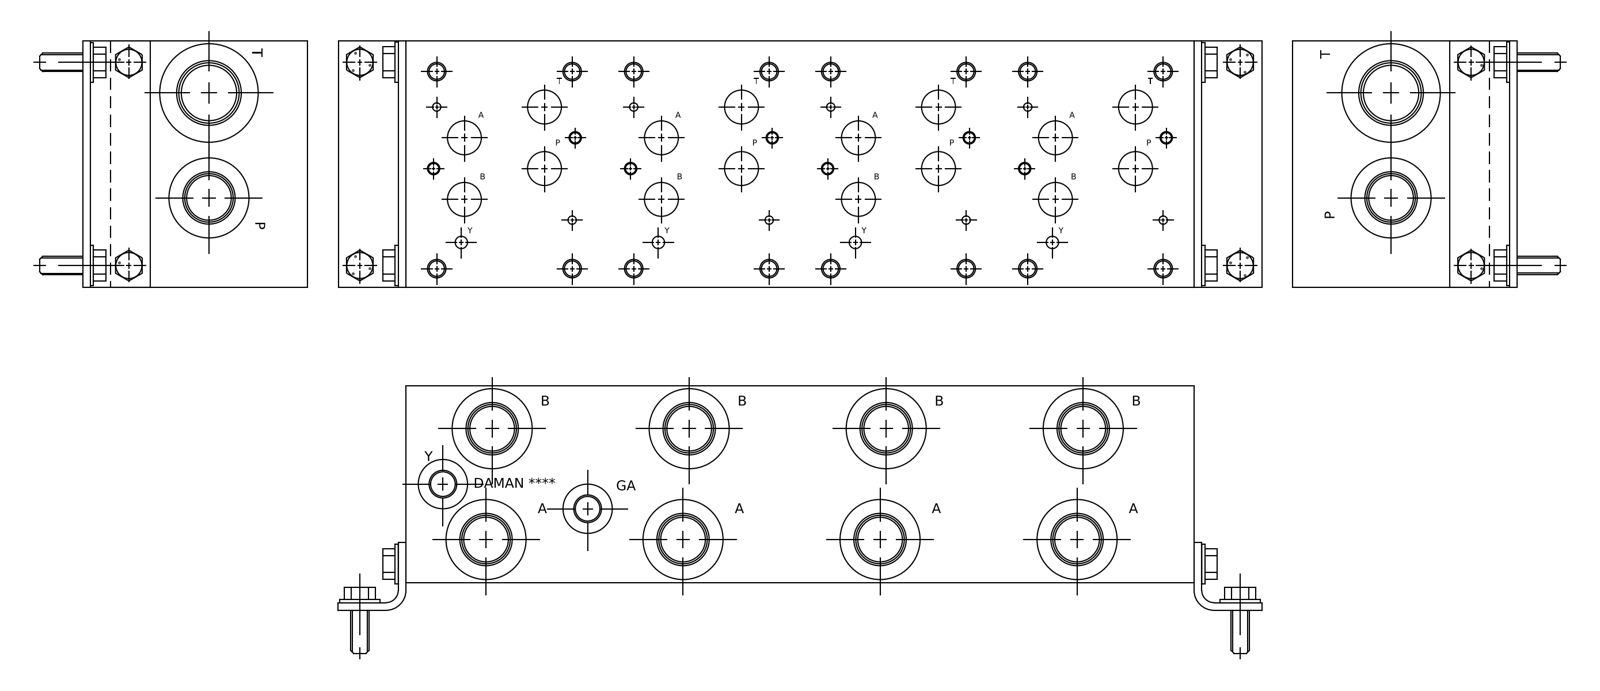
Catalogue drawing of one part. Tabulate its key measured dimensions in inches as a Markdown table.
| quantity | value |
| --- | --- |
| part name | Part_AD07P044S_3D |
| STEP written by | Autodesk Inventor 2020 (AUTOMOTIVE_DESIGN) |
| units | inches |
| bodies | 1 solid, 875 faces (456 planar, 155 cylindrical, 264 other) |
| overall size | 16 × 5 × 4 |
| volume | 300.7 in³ |
| surface area | 421.3 in² |
| round holes (diameter × count) | 0.312 × 18, 0.375 × 18, 0.906 × 9, 0.981 × 9, 1.08 × 9, 1.655 × 9, 0.172 × 8, 0.201 × 8, 0.25 × 8, 0.656 × 8, 0.688 × 8, 1.063 × 7 |
| main face-to-face distances | 4, 5, 0.031, 16, 4.969, 15.969, 15.938, 0.75, 0.781, 4.219 |
| hole center spacings | 4, 8, 1.741, 4.191, 2.456, 5.659, 1.25, 8.097 |
